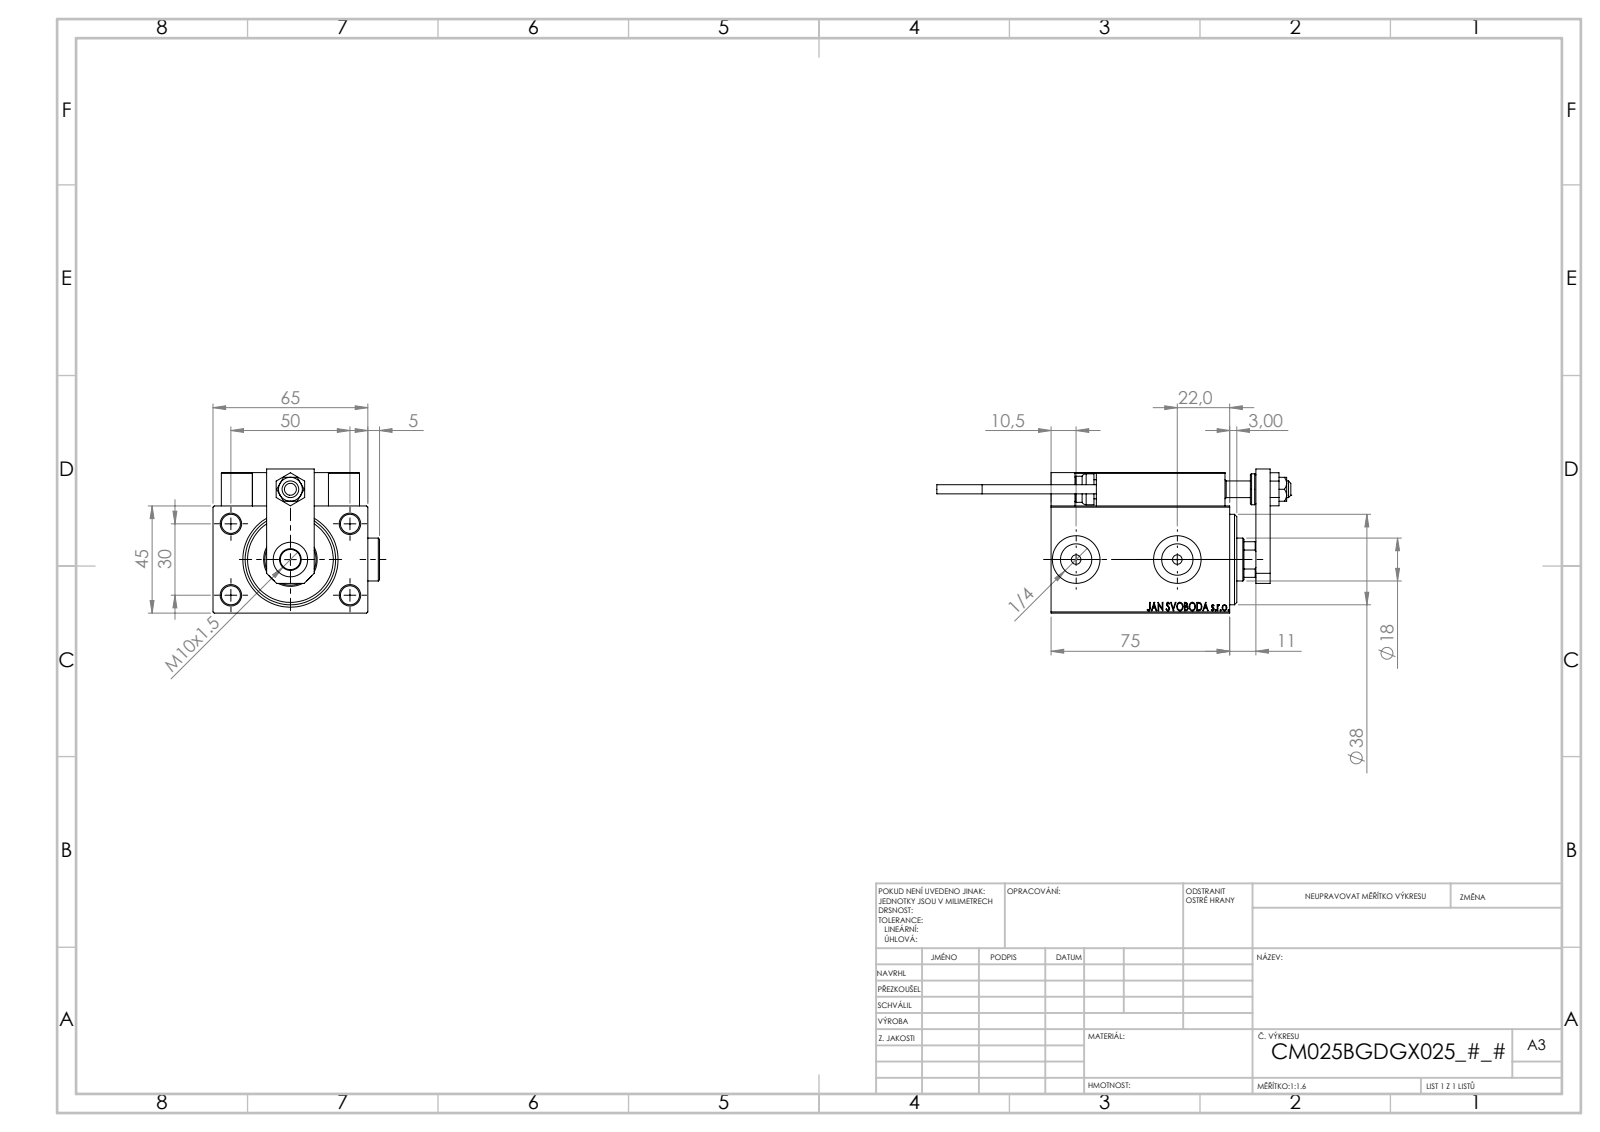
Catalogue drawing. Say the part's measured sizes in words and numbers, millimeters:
The part is named "V450CM_B_Body; KONCOVKA; ALLEN BOLT D5; Zatka_OIL_PORT (+7 more)". Its 3-D file was written by "SolidWorks 2019 (CONFIG_CONTROL_DESIGN)". It is 26 solids with 1372 faces: 595 planar, 200 cylindrical and 577 other. Overall it measures 148.7 by 69.9 by 60.5 millimeters. Its volume is 251 190 cubic millimeters and its surface area 69 115 square millimeters. Round holes: 9 of diameter 8, 6 of diameter 4, 4 of diameter 3.2, 2 of diameter 5, 2 of diameter 13.16, 2 of diameter 20, 1 of diameter 7, 1 of diameter 8.5, 1 of diameter 14.5, 1 of diameter 18, 1 of diameter 21.5, 1 of diameter 22.5. Round bosses or shafts: 2 of diameter 18, 2 of diameter 5, 2 of diameter 3.8, 1 of diameter 13, 1 of diameter 11. Partial cylindrical surfaces (rounded edges, fillets, slot ends): 30 of radius 0.3, 2 of radius 3, 1 of radius 8.5. The main face-to-face distances are 45, 14, 65, 6, 59, 13, 19, 5, 3.5, 86. The hole center spacings are 29.15, 11.37, 20, 27.07, 28.9, 29.59, 29.69, 30.
